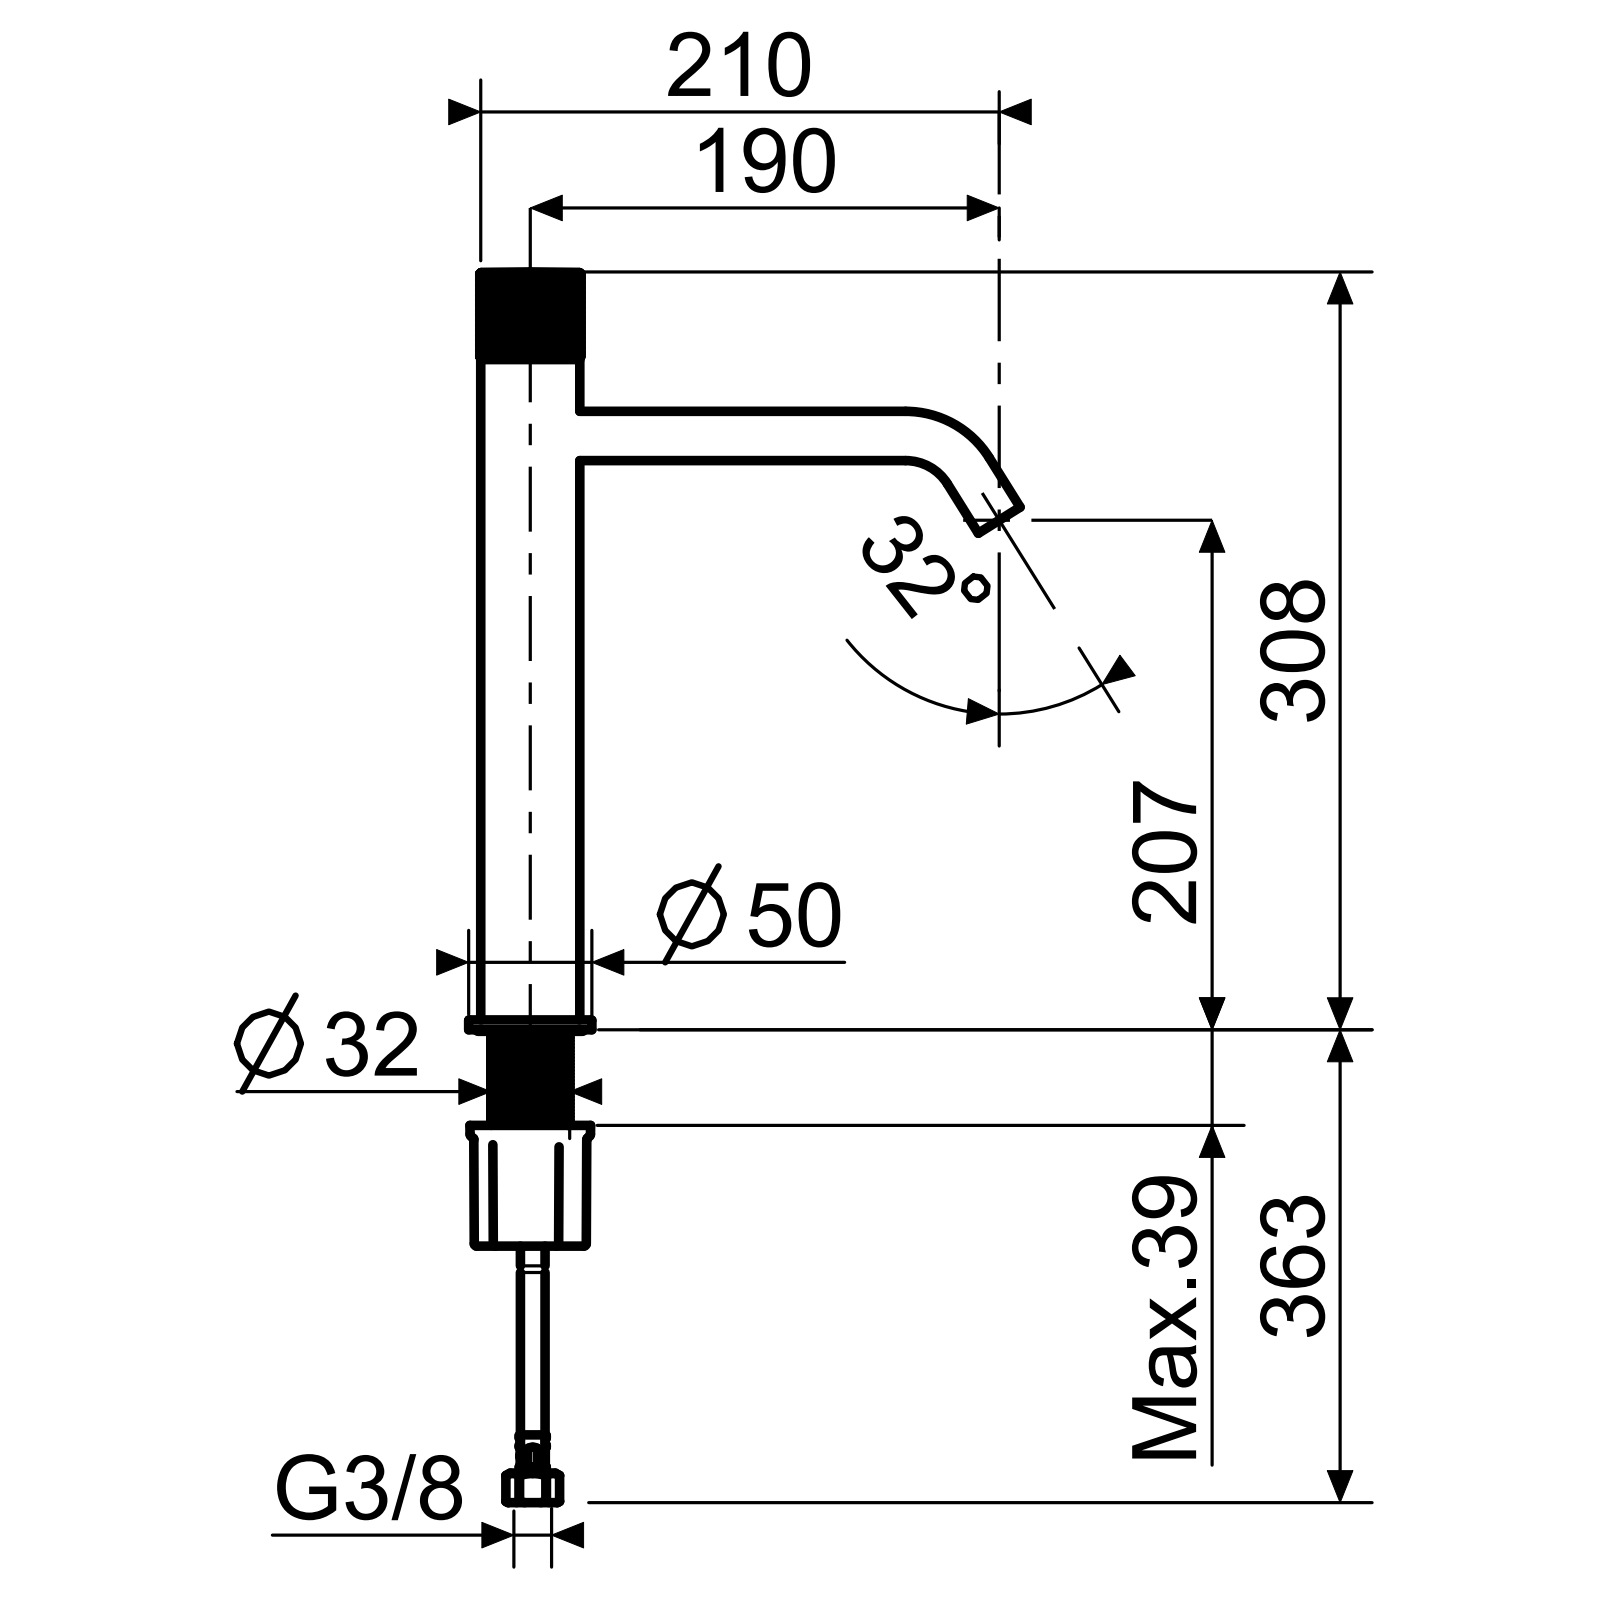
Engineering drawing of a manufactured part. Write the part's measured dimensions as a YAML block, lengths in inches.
part_name: "ALOG222C001; ALOG007C002; ALOG222W001; SCCMAC0007 (+4 more)"
step_written_by: "CREO PARAMETRIC BY PTC INC, 2022164 (CONFIG_CONTROL_DESIGN)"
units: inches
bodies: {solids: 7, faces: 6552, planar: 2903, cylindrical: 1279, other: 2370}
overall_size: [12.109, 8.811, 1.969]
volume: 8.798
surface_area: 174.9
round_holes:
  - {diameter: 0.165, count: 1}
  - {diameter: 0.201, count: 1}
  - {diameter: 0.354, count: 1}
  - {diameter: 0.406, count: 1}
  - {diameter: 0.433, count: 1}
  - {diameter: 0.478, count: 1}
  - {diameter: 0.573, count: 1}
  - {diameter: 0.591, count: 1}
  - {diameter: 0.612, count: 1}
  - {diameter: 0.659, count: 1}
  - {diameter: 0.984, count: 1}
  - {diameter: 1.181, count: 1}
round_bosses_or_shafts:
  - {diameter: 0.787, count: 2}
  - {diameter: 1.969, count: 1}
  - {diameter: 1.583, count: 1}
  - {diameter: 1.575, count: 1}
  - {diameter: 1.488, count: 1}
  - {diameter: 1.26, count: 1}
  - {diameter: 0.709, count: 1}
  - {diameter: 0.65, count: 1}
partial_cylinders:
  - {radius: 0.039, count: 2}
  - {radius: 0.098, count: 2}
  - {radius: 0.118, count: 2}
  - {radius: 0.059, count: 1}
  - {radius: 0.157, count: 1}
  - {radius: 0.245, count: 1}
  - {radius: 0.256, count: 1}
  - {radius: 0.297, count: 1}
face_to_face_distances: [0.079, 0.157, 12, 11.843, 1.119, 11.921, 8.061, 7.982, 7.904, 3.939]
